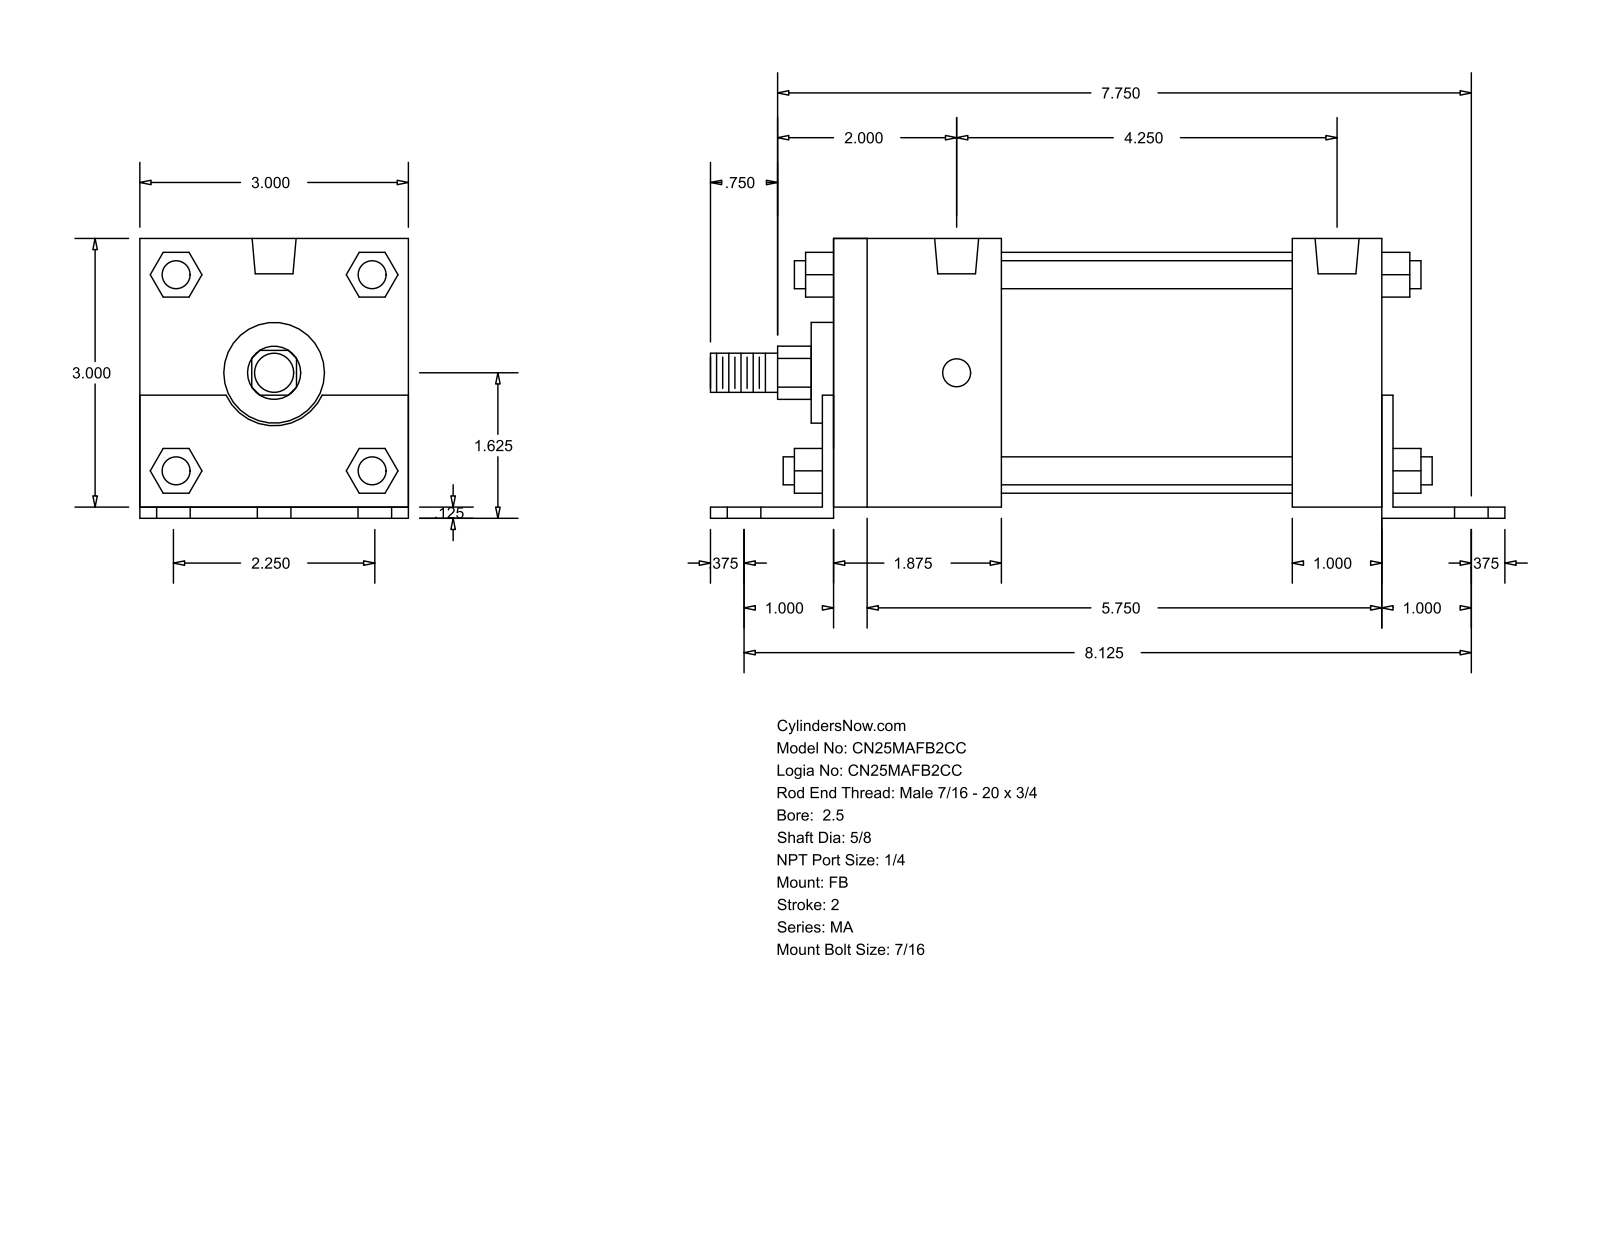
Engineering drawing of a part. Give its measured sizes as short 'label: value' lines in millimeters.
name: MA_FB__0250_0.625
written by: GSSL Pune (CONFIG_CONTROL_DESIGN)
unit: mm
bodies: 0 solids, 140 faces (105 planar, 35 cylindrical, 0 other)
size: 225.43 × 79.38 × 76.2
holes: 6× ⌀11.11, 4× ⌀7.94, 2× ⌀12.49
bosses: 4× ⌀7.94, 1× ⌀68.33, 1× ⌀28.57, 1× ⌀15.88, 1× ⌀11.11
rounds: 1× R7.54, 1× R15.05
face distances: 76.2, 3.17, 79.37, 155.57, 161.92, 3.18, 82.55, 158.74, 47.62, 25.4
hole spacings: 28.57, 208.35, 206.38, 47.62, 57.14, 66.75, 107.95, 148.82
